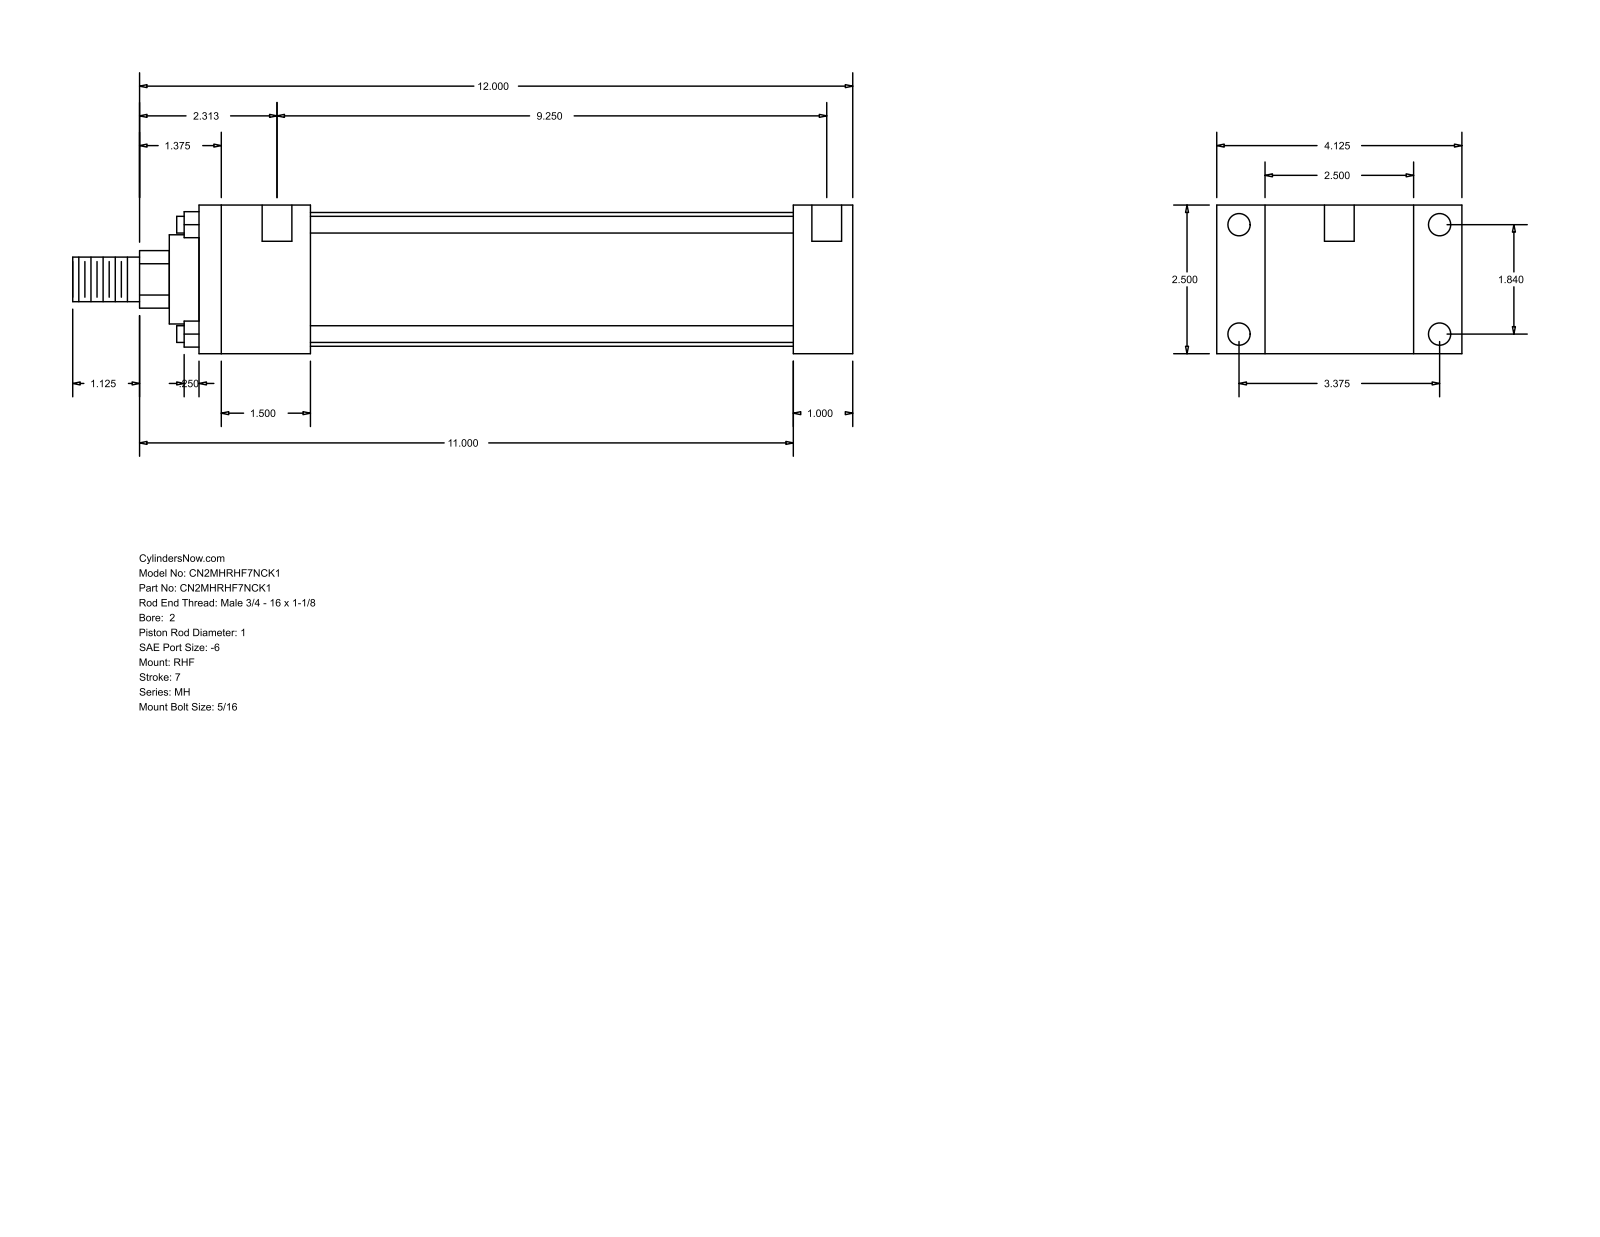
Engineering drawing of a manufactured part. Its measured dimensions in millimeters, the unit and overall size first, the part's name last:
Units: millimetres
Overall size (bounding box): 333.38 × 104.78 × 63.5
Round holes (diameter × count): ⌀5.56 ×4, ⌀9.53 ×4, ⌀12.7 ×2
Round bosses / shafts (diameter × count): ⌀7.14 ×4, ⌀57.15 ×1, ⌀38.1 ×1, ⌀25.4 ×1, ⌀19.05 ×1
Partial cylindrical surfaces — rounded edges, fillets, slot ends (radius × count): R12.29 ×1
Main face-to-face distances: 63.5, 25.4, 20.64, 84.14, 279.4, 254, 104.78, 47.63, 206.37, 231.77
Hole centre spacings: 46.74, 85.72, 97.63, 242.88, 3.17, 4.76, 234.95, 238.12
Bodies: 0 solids, 88 faces (60 planar, 28 cylindrical, 0 other)
Part name (STEP PRODUCT): MH_RHF__0200_1
STEP written by: GSSL Pune (CONFIG_CONTROL_DESIGN)
